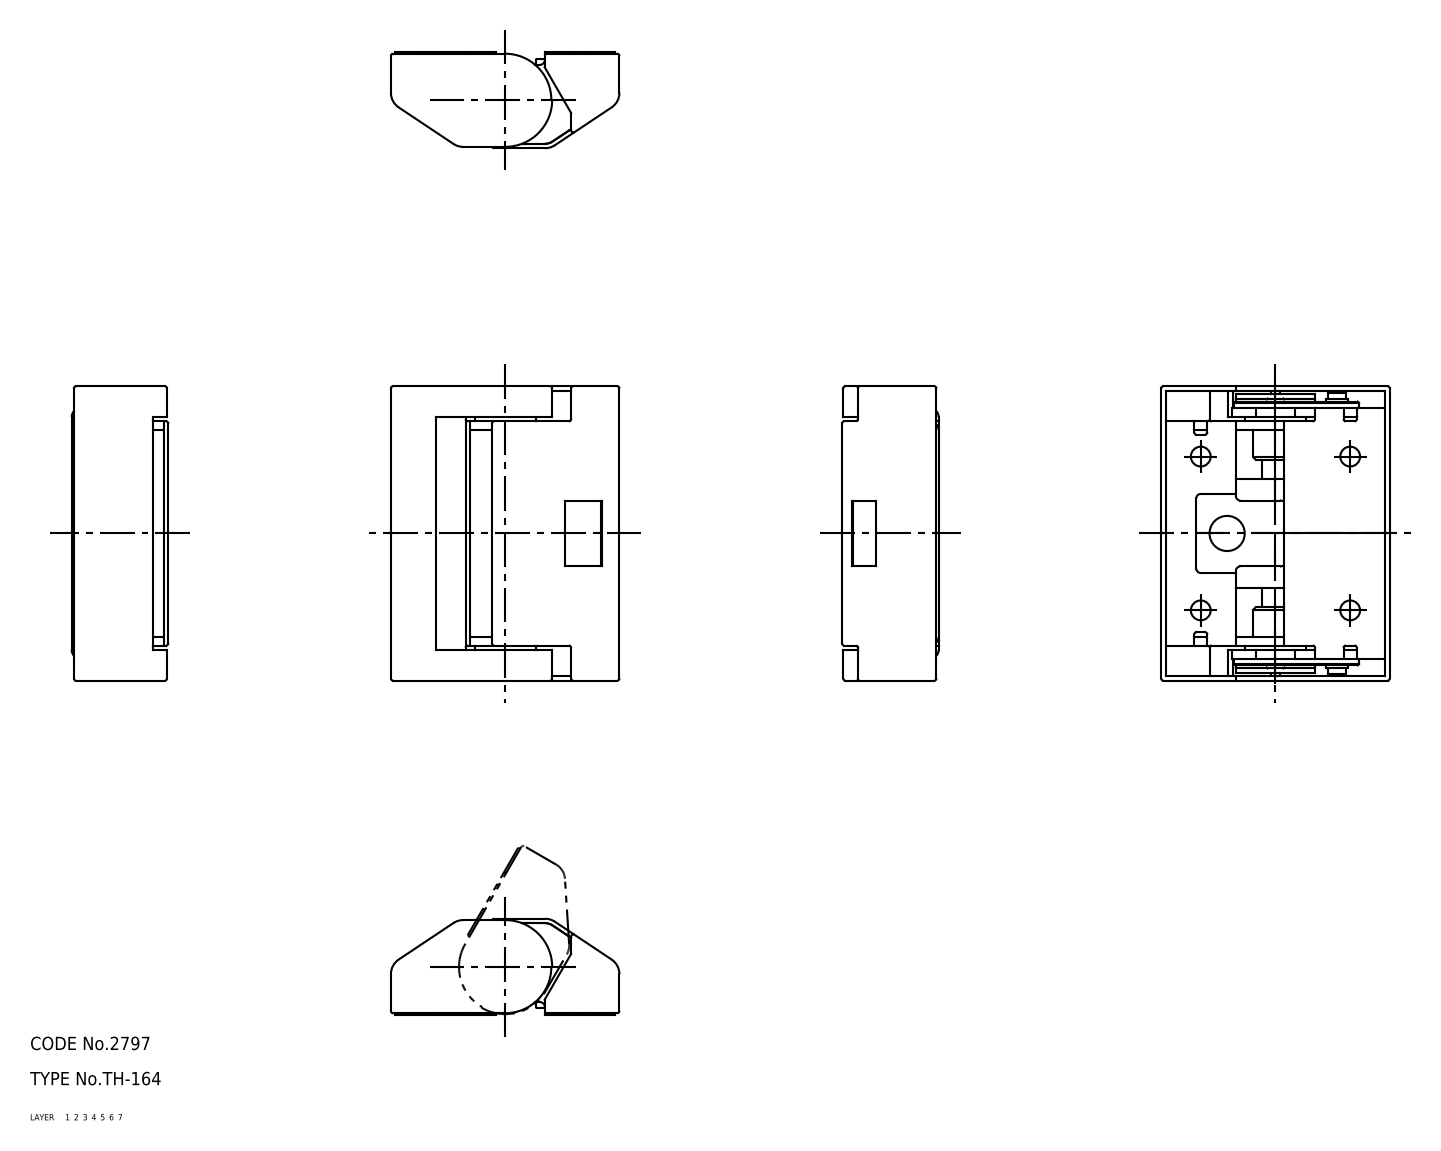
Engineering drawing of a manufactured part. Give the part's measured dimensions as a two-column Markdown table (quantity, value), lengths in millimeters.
| quantity | value |
| --- | --- |
| part name | 67125237; 67125250; 67125263; 67125276 |
| STEP written by | CADfix (AUTOMOTIVE_DESIGN) |
| units | millimeters |
| bodies | 4 solids, 334 faces (0 planar, 0 cylindrical, 334 other) |
| overall size | 67 × 52 × 22 |
| volume | 24 193 mm³ |
| surface area | 32 129 mm² |
